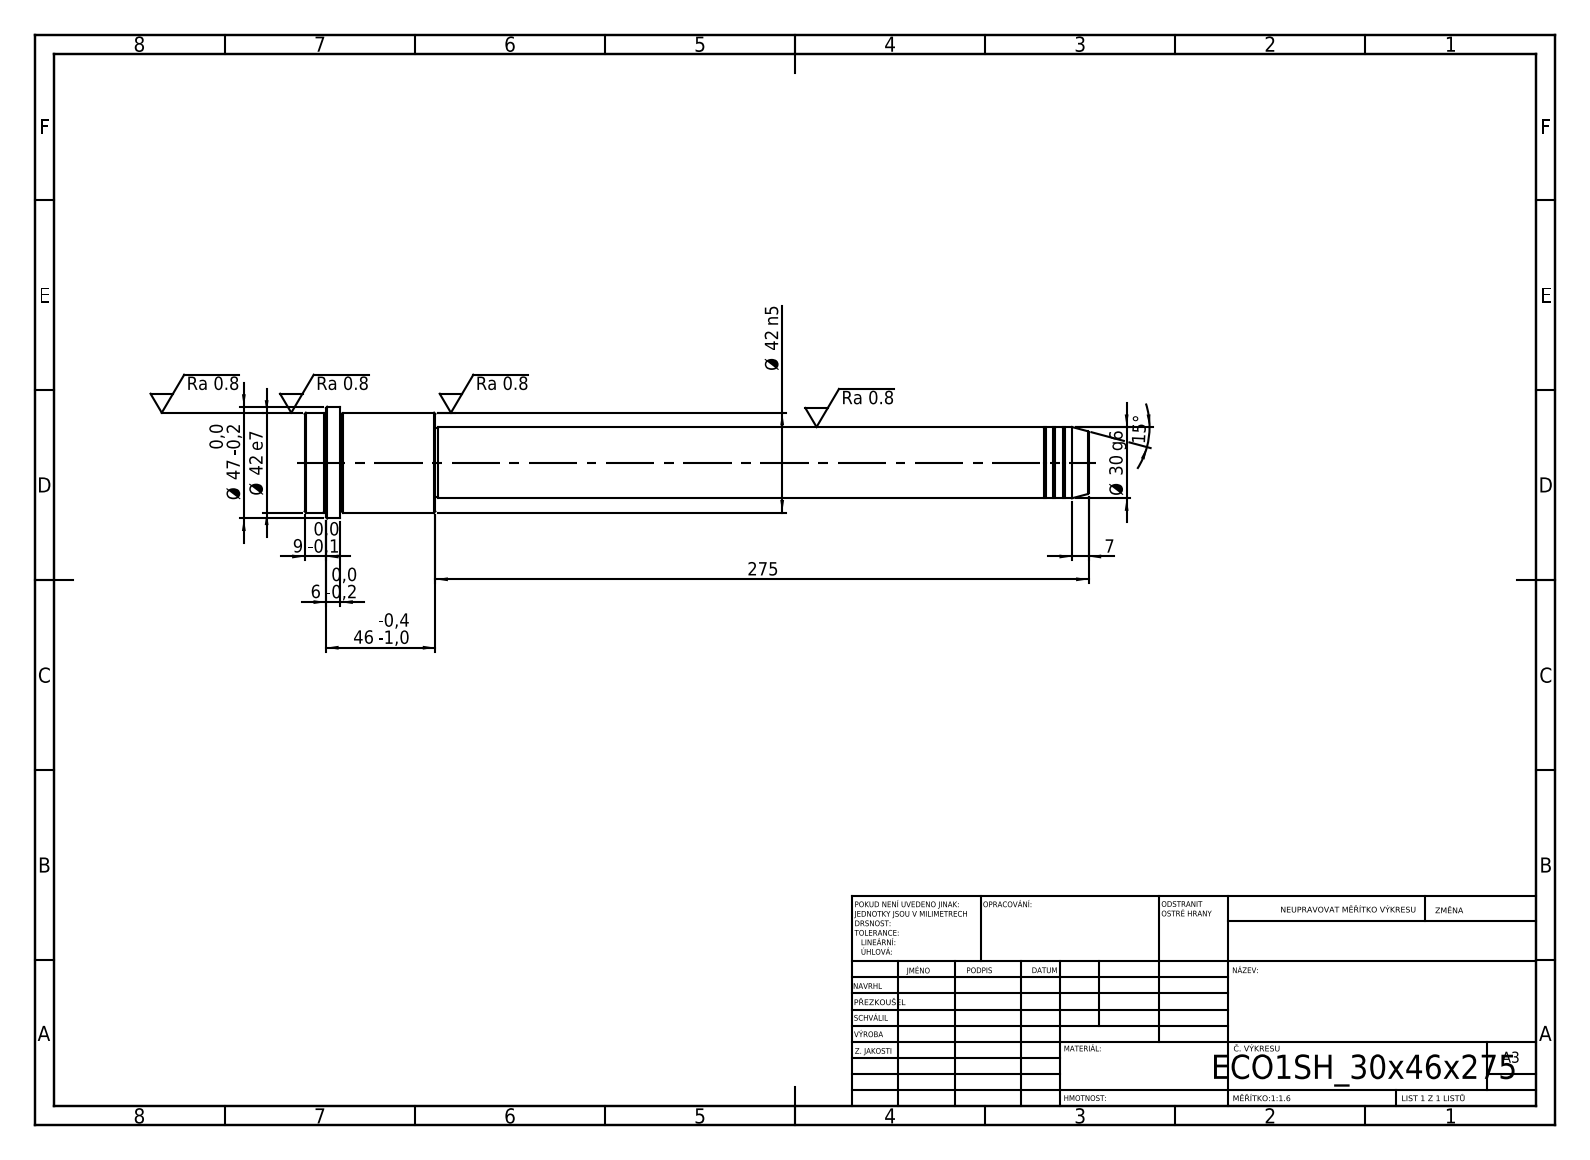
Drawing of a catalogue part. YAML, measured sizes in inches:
step_written_by: "SolidWorks 2019 (CONFIG_CONTROL_DESIGN)"
units: inches
bodies: {solids: 1, faces: 52, planar: 6, cylindrical: 16, other: 30}
overall_size: [12.992, 1.85, 1.85]
volume: 16.58
surface_area: 57.05
round_bosses_or_shafts:
  - {diameter: 1.85, count: 1}
  - {diameter: 1.654, count: 1}
  - {diameter: 1.181, count: 1}
  - {diameter: 1.142, count: 1}
face_to_face_distances: [2.165, 10.827, 12.992, 12.402, 1.575, 0.591, 12.638, 1.811, 0.236, 0.354]
